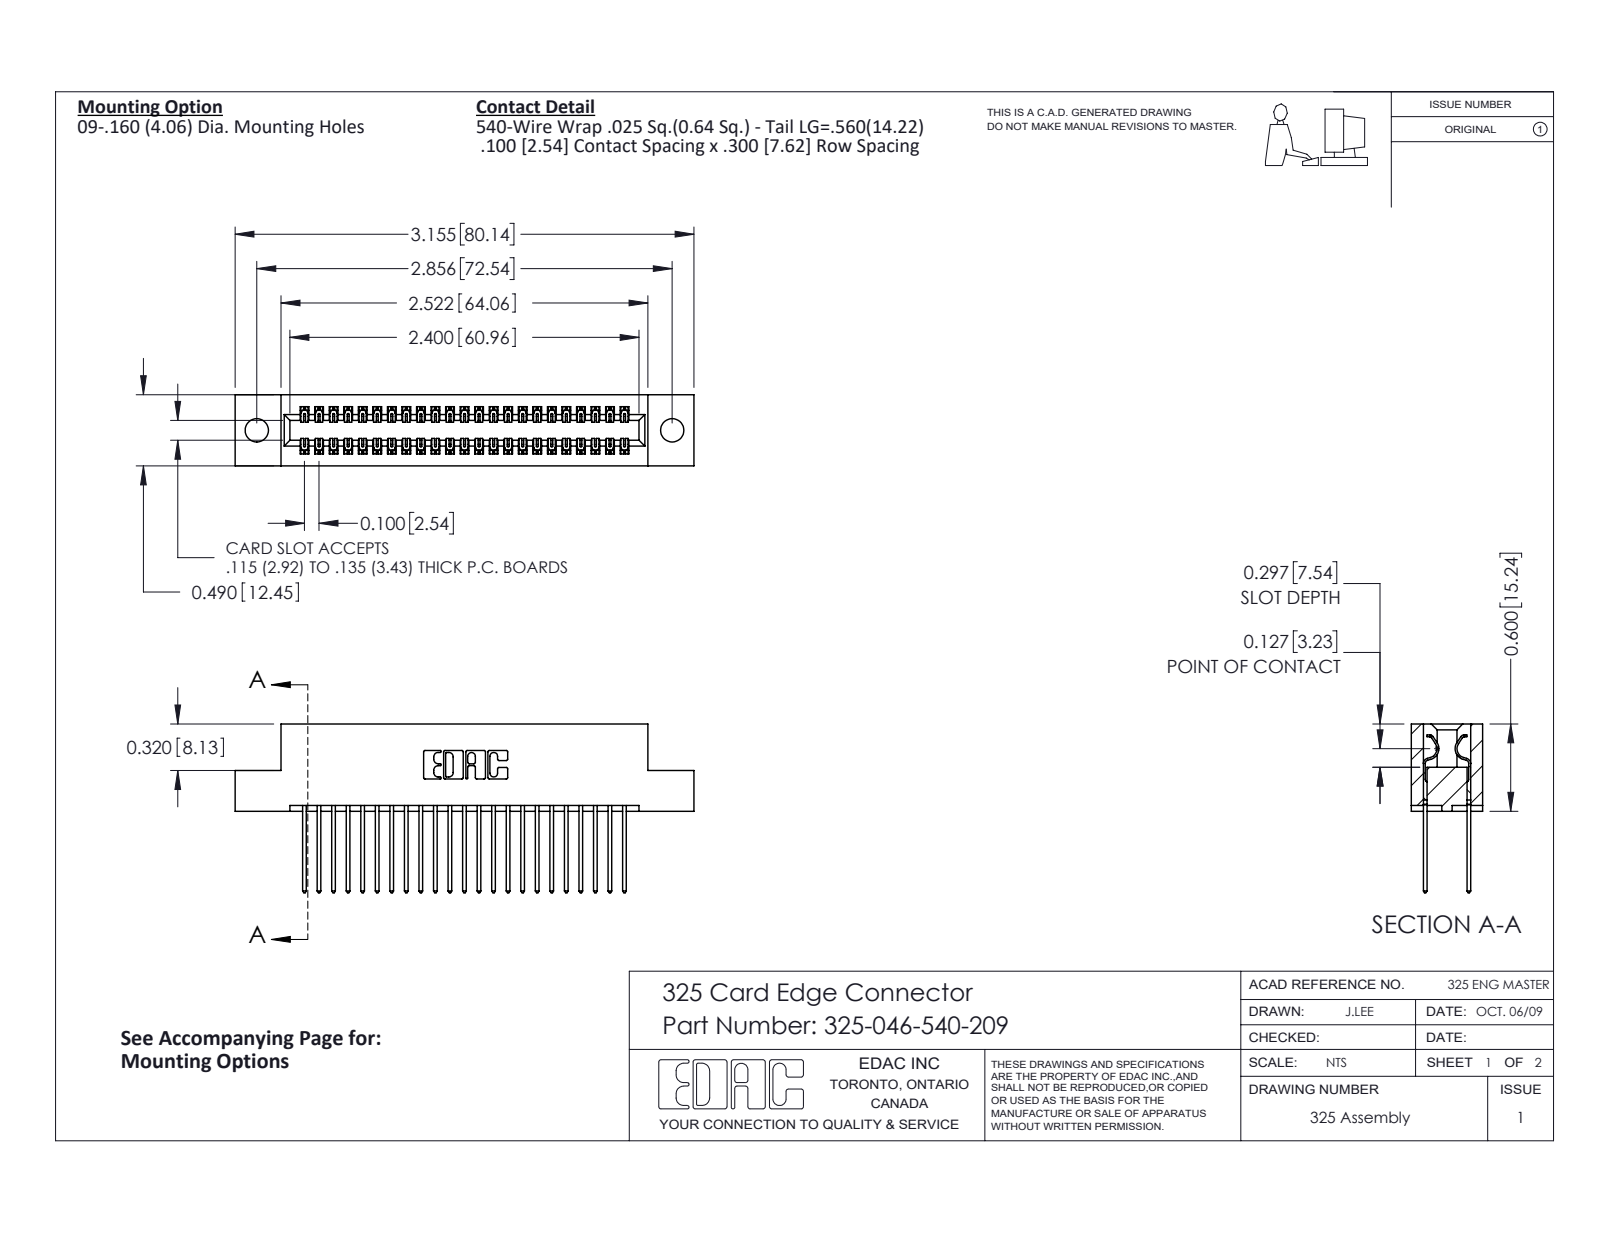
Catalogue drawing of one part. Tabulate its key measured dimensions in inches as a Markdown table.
| quantity | value |
| --- | --- |
| part name | 325 Part_.160 TH; 325-046-540-209; 325-292-001_325-293-140 |
| STEP written by | SolidWorks 2016 (CONFIG_CONTROL_DESIGN) |
| units | inches |
| bodies | 47 solids, 2506 faces (1726 planar, 780 cylindrical, 0 other) |
| overall size | 3.155 × 1.16 × 0.49 |
| volume | 0.617 in³ |
| surface area | 19.45 in² |
| round holes (diameter × count) | 0.16 × 2 |
| partial cylindrical surfaces (radius × count) | 0.006 × 69, 0.01 × 46, 0.01 × 22, 0.007 × 6, 0.031 × 6, 0.026 × 3, 0.014 × 2, 0.022 × 2 |
| main face-to-face distances | 0.083, 0.407, 0.3, 0.107, 0.383, 0.025, 0.49, 0.325, 0.275, 0.04 |
| hole center spacings | 2.856 |
